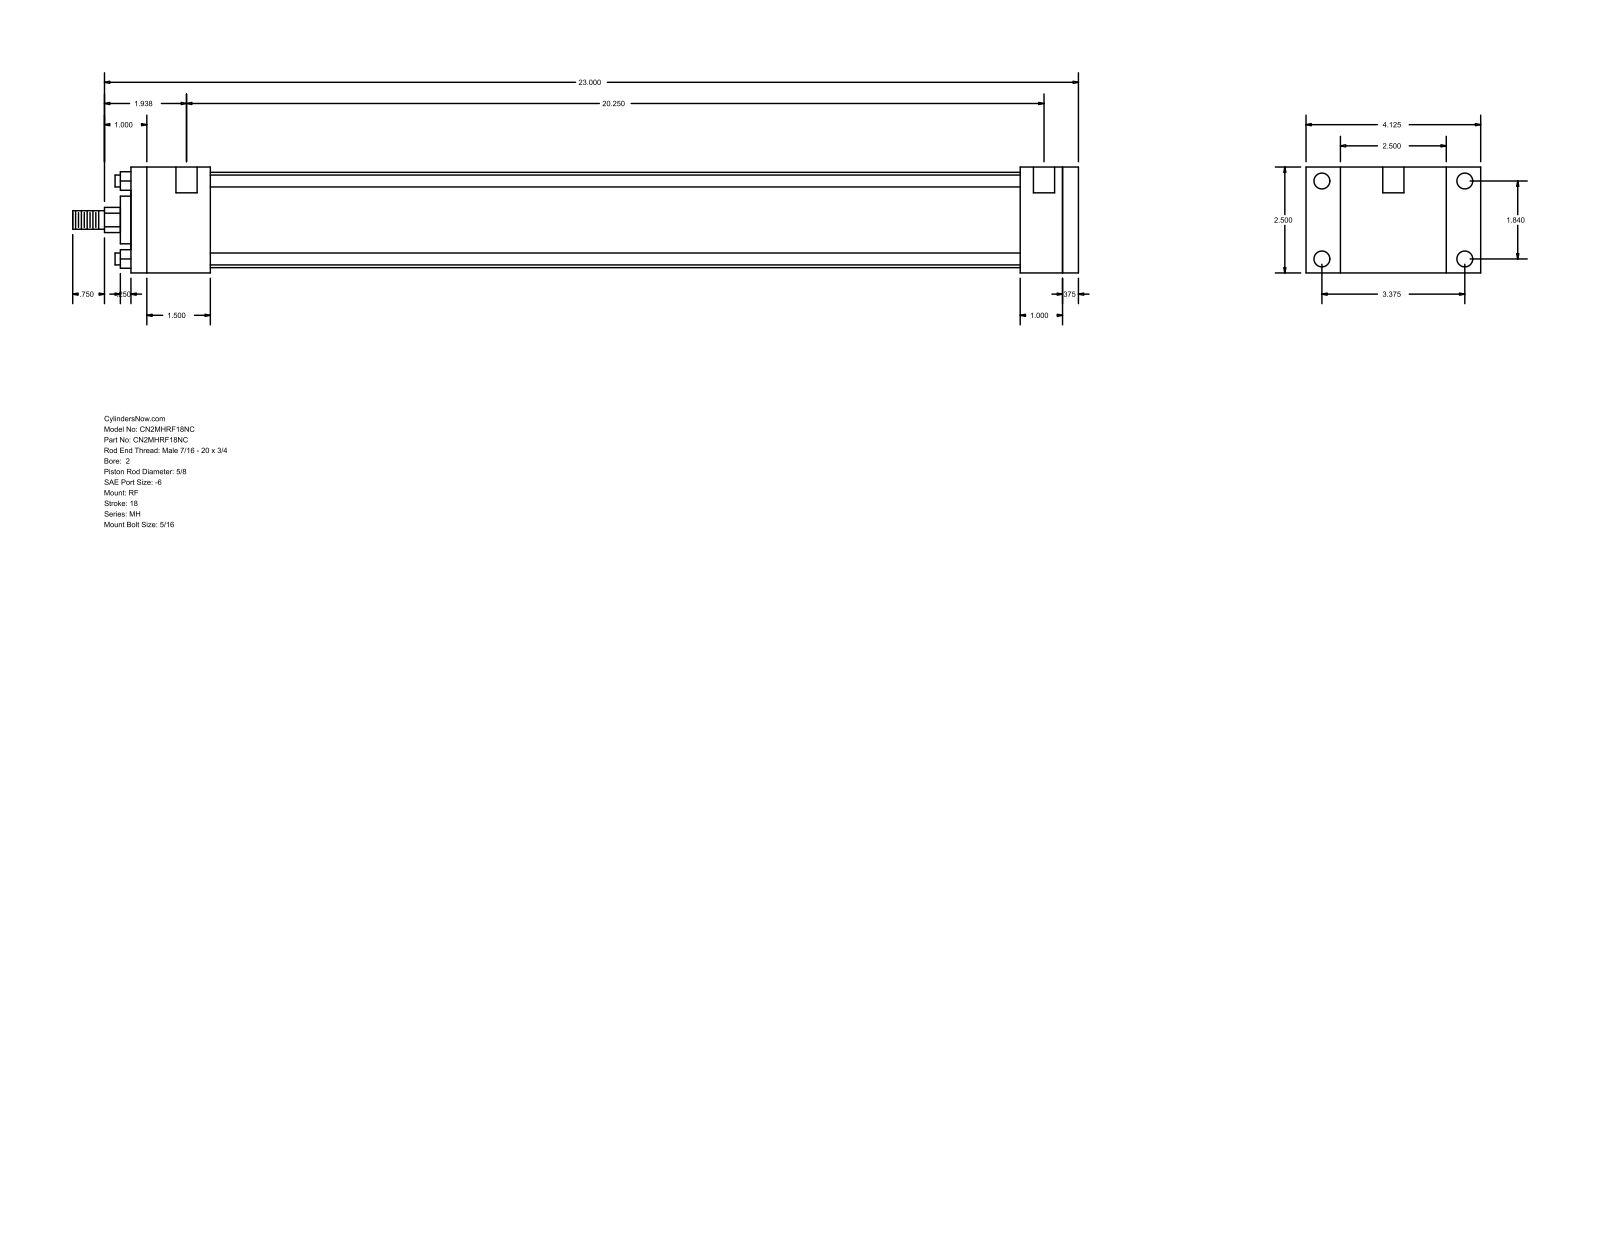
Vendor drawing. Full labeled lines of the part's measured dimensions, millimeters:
Part name (STEP PRODUCT): MH_RF__0200_0.625
STEP written by: GSSL Pune (CONFIG_CONTROL_DESIGN)
Units: millimetres
Bodies: 0 solids, 92 faces (64 planar, 28 cylindrical, 0 other)
Overall size (bounding box): 603.25 × 104.78 × 63.5
Round holes (diameter × count): ⌀5.56 ×4, ⌀9.53 ×4, ⌀12.7 ×2
Round bosses / shafts (diameter × count): ⌀7.14 ×4, ⌀57.15 ×1, ⌀28.57 ×1, ⌀15.88 ×1, ⌀11.11 ×1
Partial cylindrical surfaces — rounded edges, fillets, slot ends (radius × count): R7.54 ×1
Main face-to-face distances: 63.5, 568.32, 9.53, 558.79, 25.4, 34.93, 47.62, 533.39, 485.77, 511.17
Hole centre spacings: 46.74, 85.72, 97.63, 522.29, 3.18, 4.76, 514.35, 517.53
